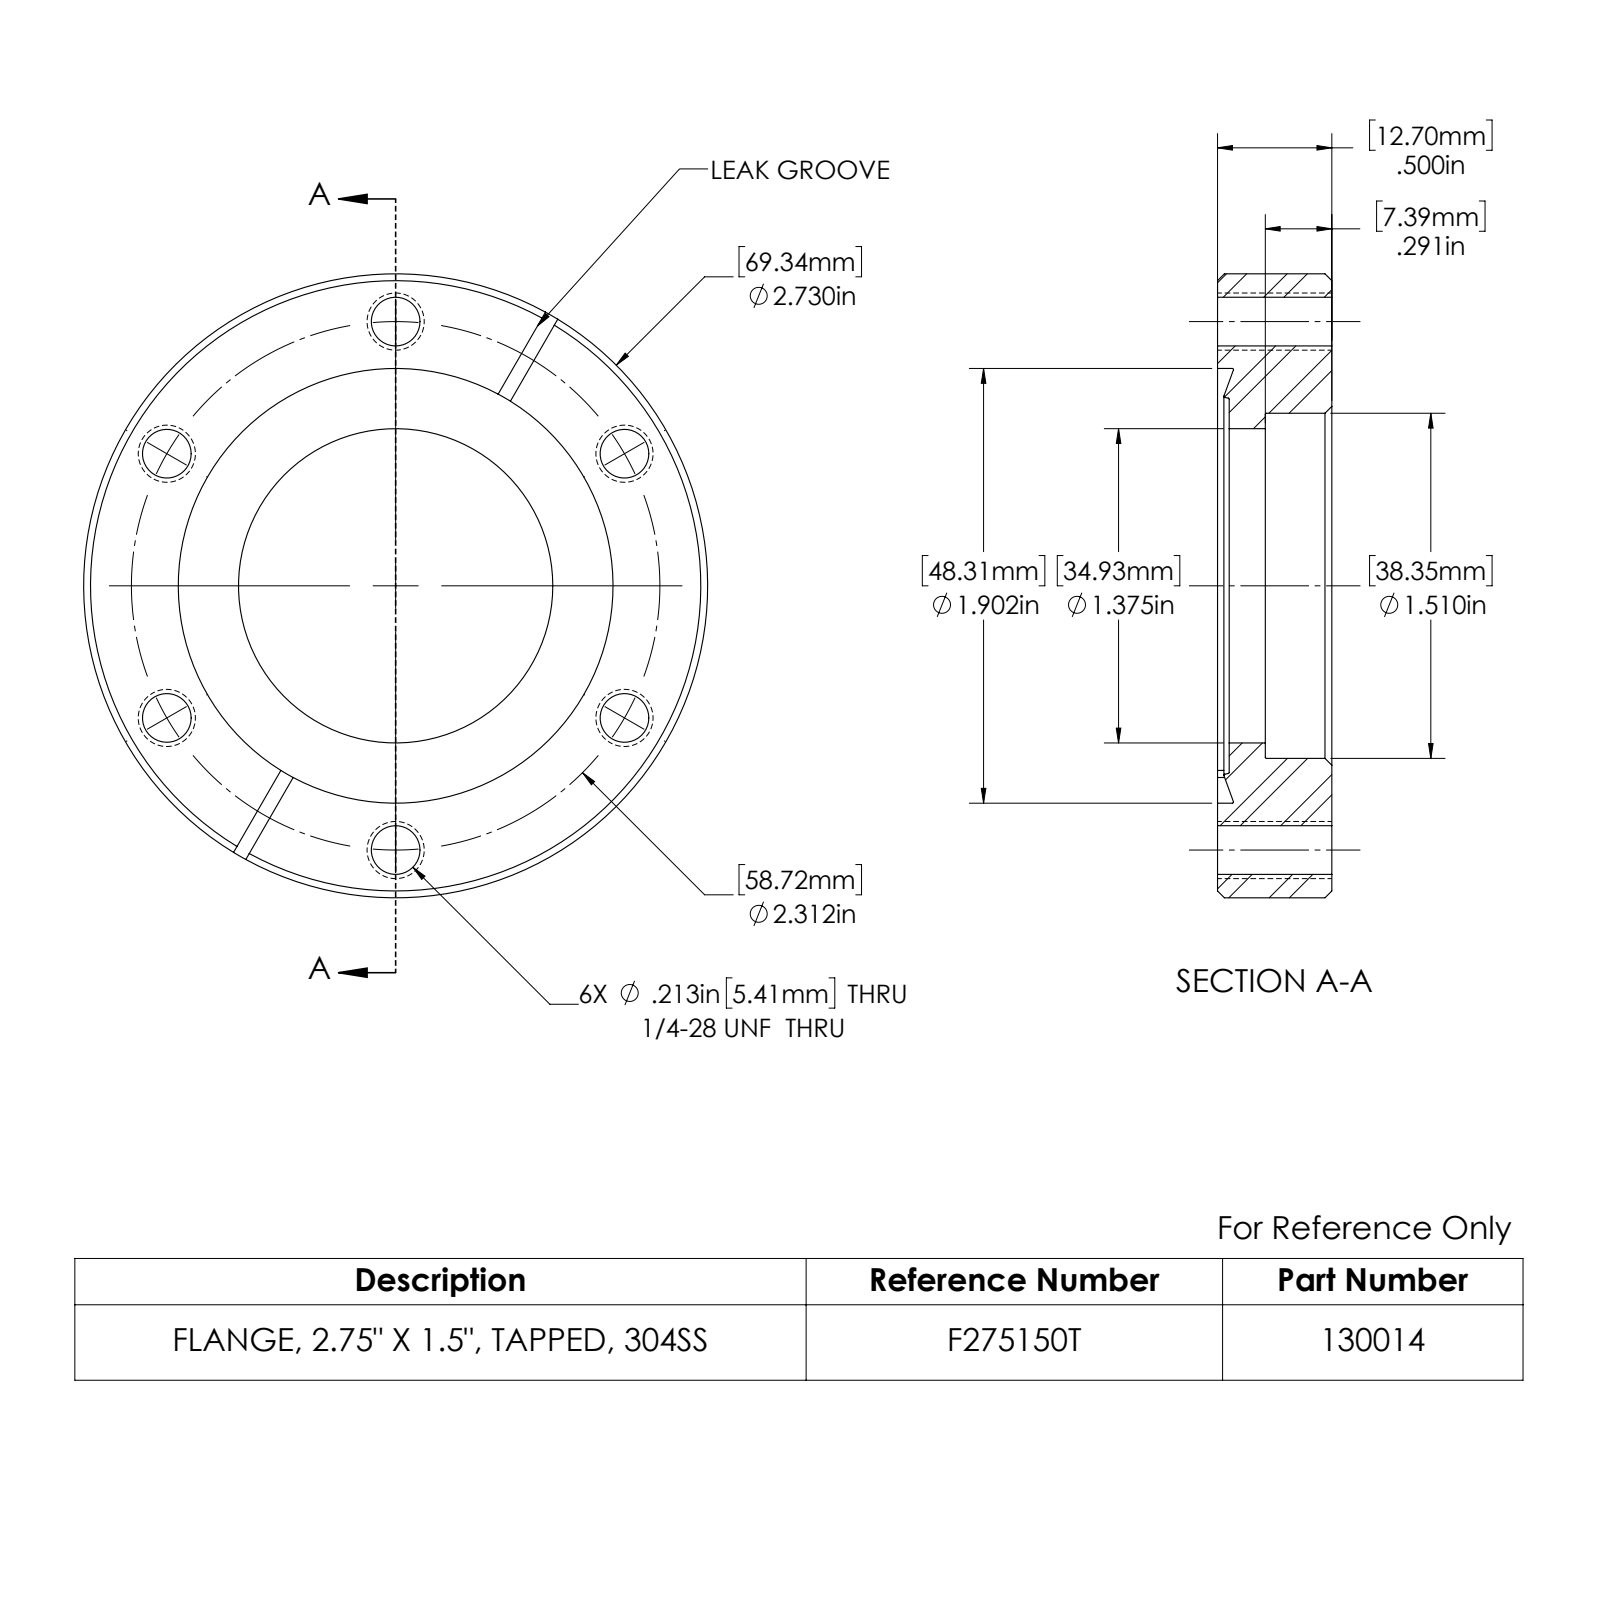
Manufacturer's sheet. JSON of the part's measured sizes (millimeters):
{"part_name": "130014", "step_written_by": "SolidWorks 2022 (AUTOMOTIVE_DESIGN)", "units": "millimeters", "bodies": {"solids": 1, "faces": 50, "planar": 11, "cylindrical": 20, "other": 19}, "overall_size": [69.3, 69.3, 12.7], "volume_mm3": 31270, "surface_area_mm2": 10890, "round_holes": [[5.4, 6], [34.9, 1], [38.4, 1], [48.3, 1]], "round_bosses_or_shafts": [[69.3, 1]], "face_to_face_distances": [12.7, 1.3, 11.4, 5.3, 4, 7.4, 1.3, 4, 11.4, 1.6], "hole_center_spacings": [29.4, 50.9, 50.9, 58.7, 58.7]}
